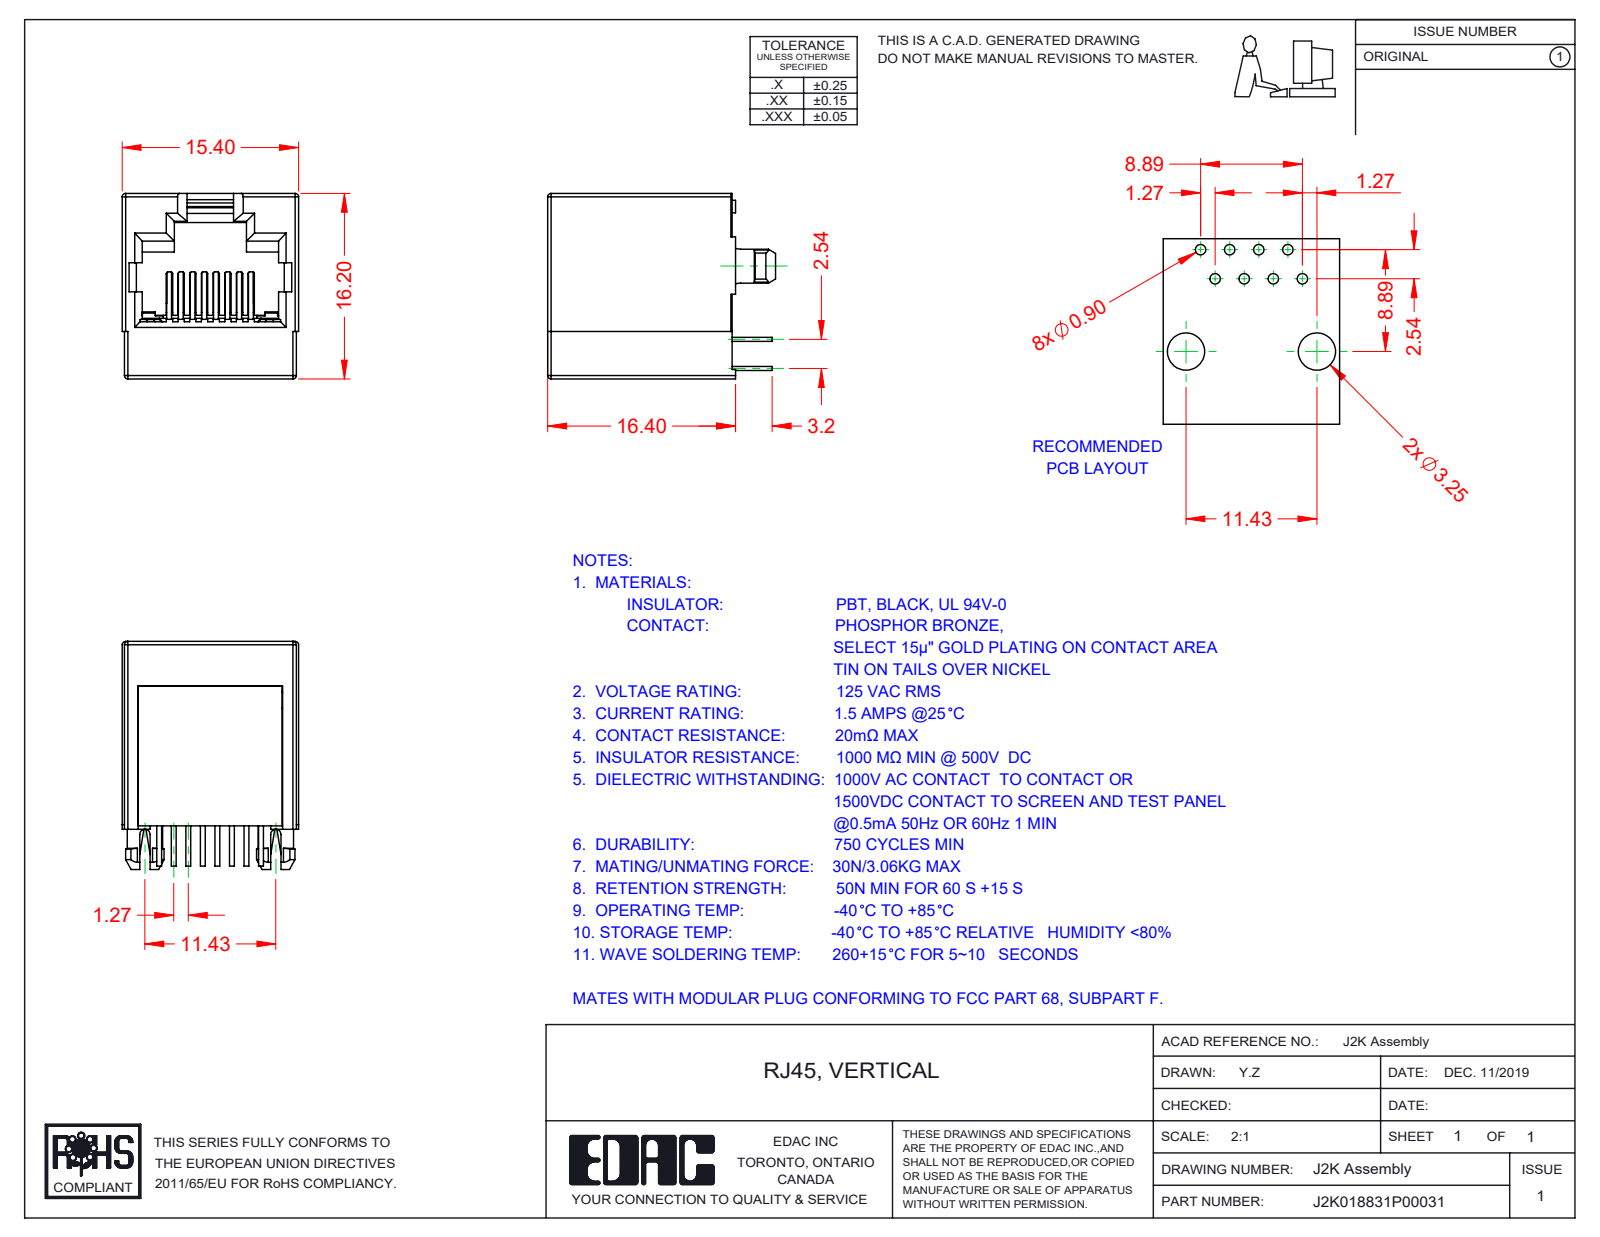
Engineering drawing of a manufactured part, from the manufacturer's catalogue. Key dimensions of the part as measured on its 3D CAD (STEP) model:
Part name (STEP PRODUCT): RJ2K018831P00031; 2K Contacts; 2K Insulator; 2K Contact Lock
STEP written by: SolidWorks 2016 (CONFIG_CONTROL_DESIGN)
Units: millimetres
Bodies: 10 solids, 723 faces (586 planar, 113 cylindrical, 24 other)
Overall size (bounding box): 19.9 × 16.2 × 15.4
Volume: 2 473 mm³ · Surface area: 3 962 mm²
Round bosses / shafts (diameter × count): ⌀3.1 ×2, ⌀1.1 ×2
Partial cylindrical surfaces — rounded edges, fillets, slot ends (radius × count): R0.15 ×16, R0.3 ×10, R0.5 ×3, R0.1 ×2, R0.2 ×2, R0.45 ×2, R0.6 ×2, R0.95 ×2
Main face-to-face distances: 16.2, 15.4, 1.4, 14, 1.2, 13.8, 15.2, 0.35, 0.5, 15
